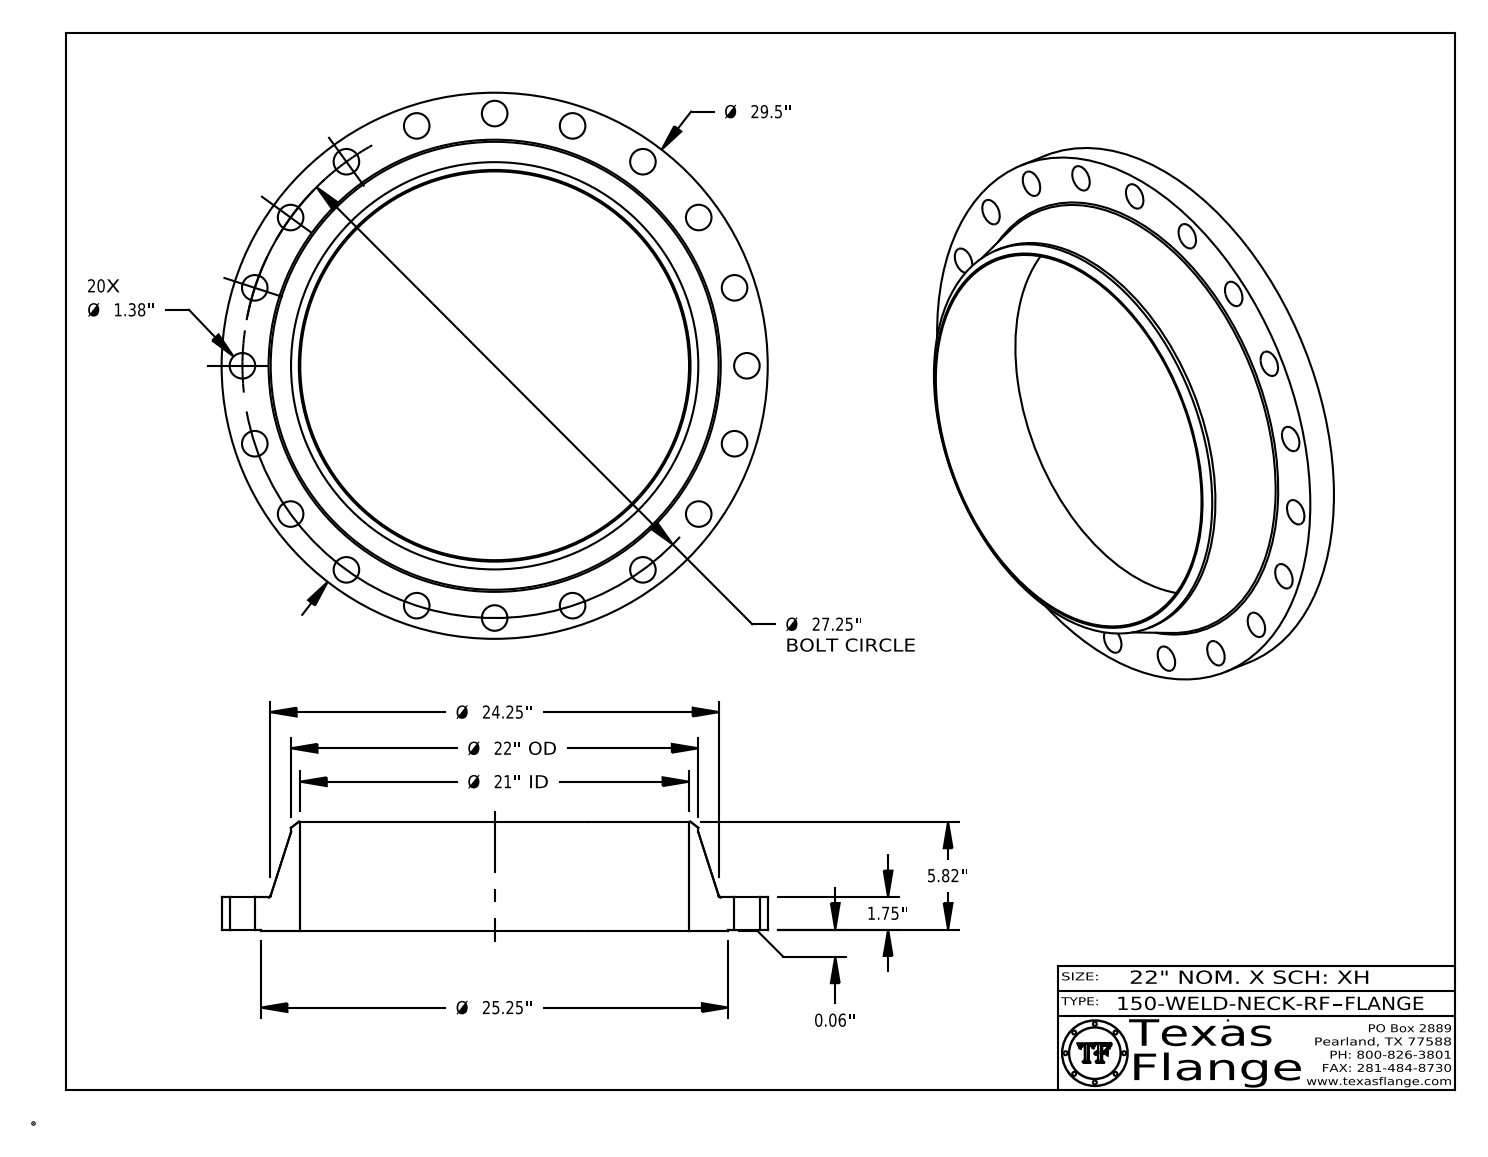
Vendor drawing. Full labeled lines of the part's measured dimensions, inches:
Part name (STEP PRODUCT): 150-WELD-NECK-RF
STEP written by: CATIA V5 STEP AP214 (AUTOMOTIVE_DESIGN)
Units: inches
Bodies: 1 solid, 443 faces (369 planar, 68 cylindrical, 6 other)
Overall size (bounding box): 29.5 × 29.5 × 5.883
Volume: 821.3 in³ · Surface area: 1 530 in²
Round holes (diameter × count): ⌀1.38 ×20, ⌀0.495 ×1, ⌀21 ×1
Round bosses / shafts (diameter × count): ⌀0.03 ×8, ⌀29.5 ×1, ⌀25.25 ×1, ⌀22 ×1, ⌀0.39 ×1
Main face-to-face distances: 1.813, 0.063, 1.75, 5.883, 5.82, 4.07, 1.798, 1.735, 0.015, 4.085
Hole centre spacings: 13.625, 19.269, 25.917, 8.421, 12.371, 4.263, 16.017, 22.046
